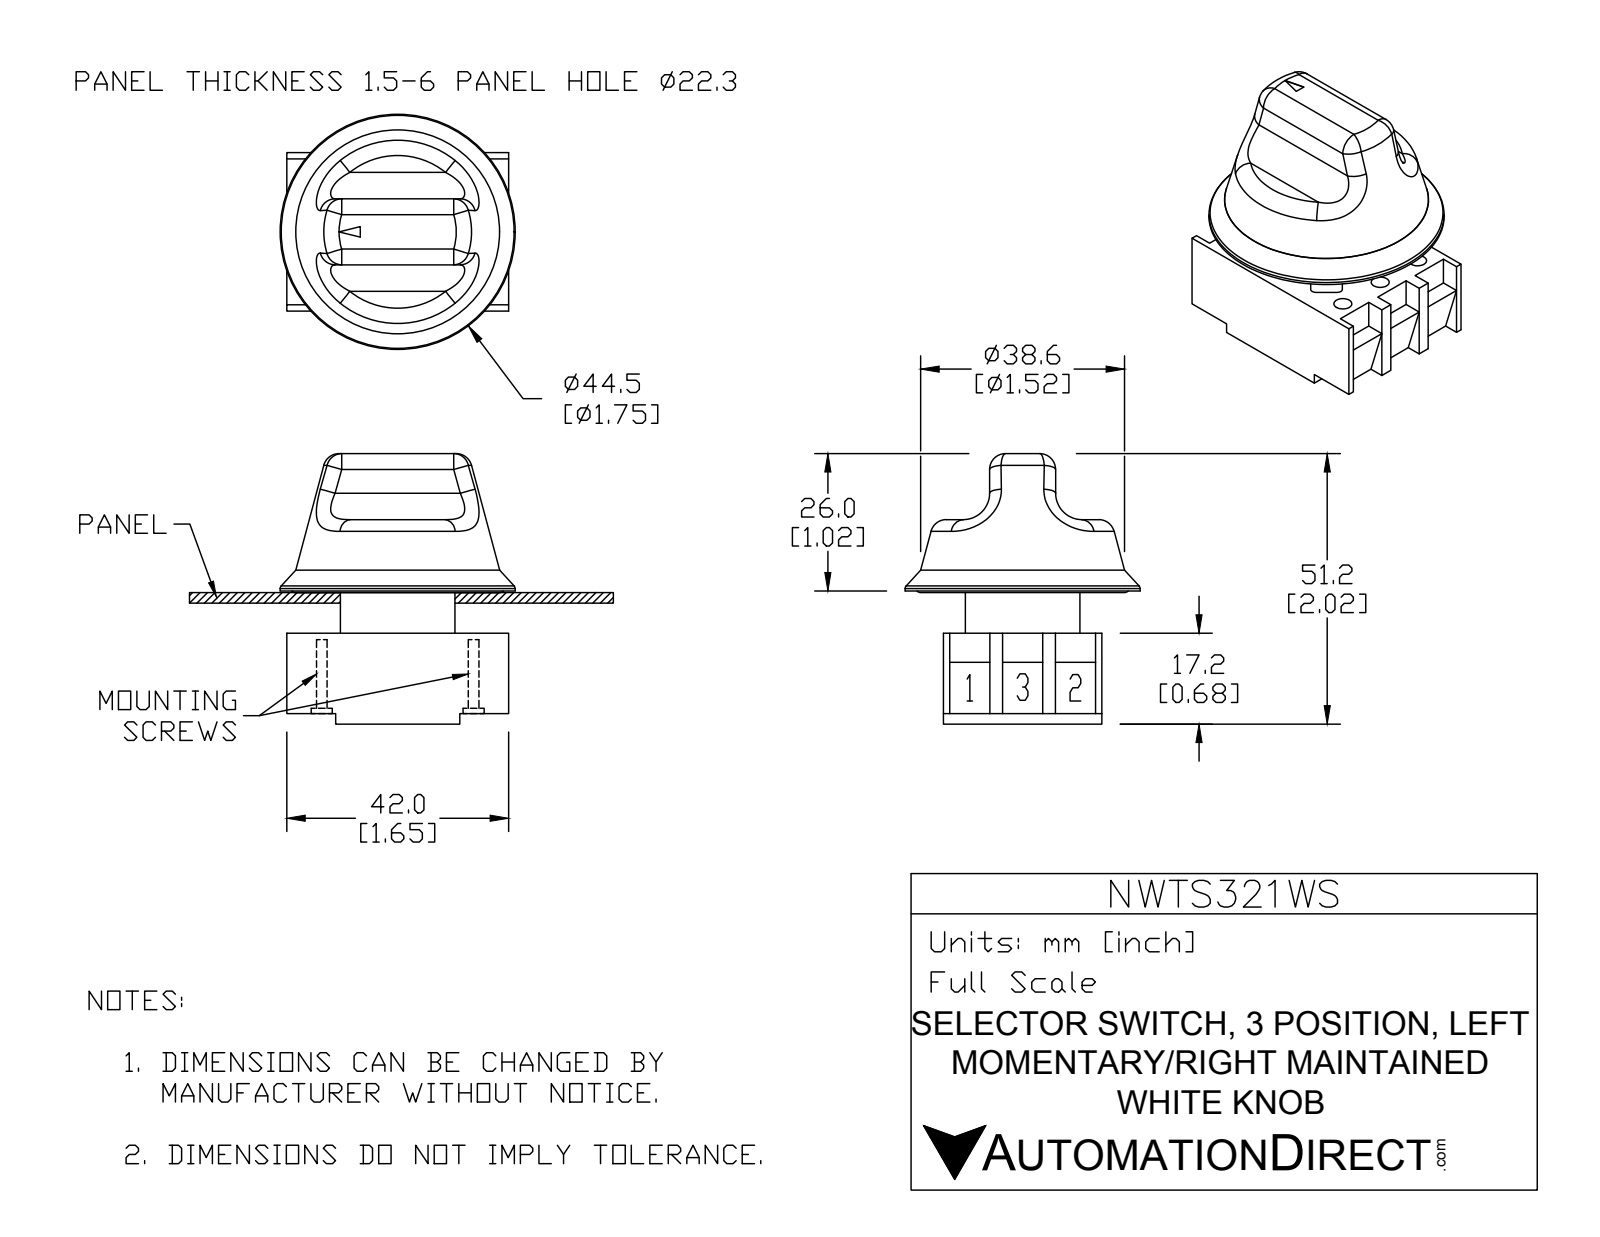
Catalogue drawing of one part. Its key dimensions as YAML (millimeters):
part_name: "NWTS321WS"
step_written_by: "SolidWorks 2015 (AUTOMOTIVE_DESIGN)"
units: millimeters
bodies: {solids: 7, faces: 236, planar: 134, cylindrical: 67, other: 35}
overall_size: [51.2, 44.5, 44.5]
volume: 35027
surface_area: 19099
round_holes:
  - {diameter: 3.4, count: 6}
  - {diameter: 5, count: 6}
  - {diameter: 12.5, count: 1}
round_bosses_or_shafts:
  - {diameter: 4.6, count: 2}
  - {diameter: 4, count: 2}
  - {diameter: 44.5, count: 1}
  - {diameter: 21.7, count: 1}
partial_cylinders:
  - {radius: 1, count: 8}
  - {radius: 8.7, count: 5}
  - {radius: 3, count: 2}
  - {radius: 5, count: 2}
  - {radius: 11, count: 1}
face_to_face_distances: [3.95, 30, 8, 11.95, 7.7, 4.25, 10, 15.2, 22.9, 23.2]
hole_center_spacings: [10, 17.52, 30.45, 28.76, 14.38, 20, 35.03]
